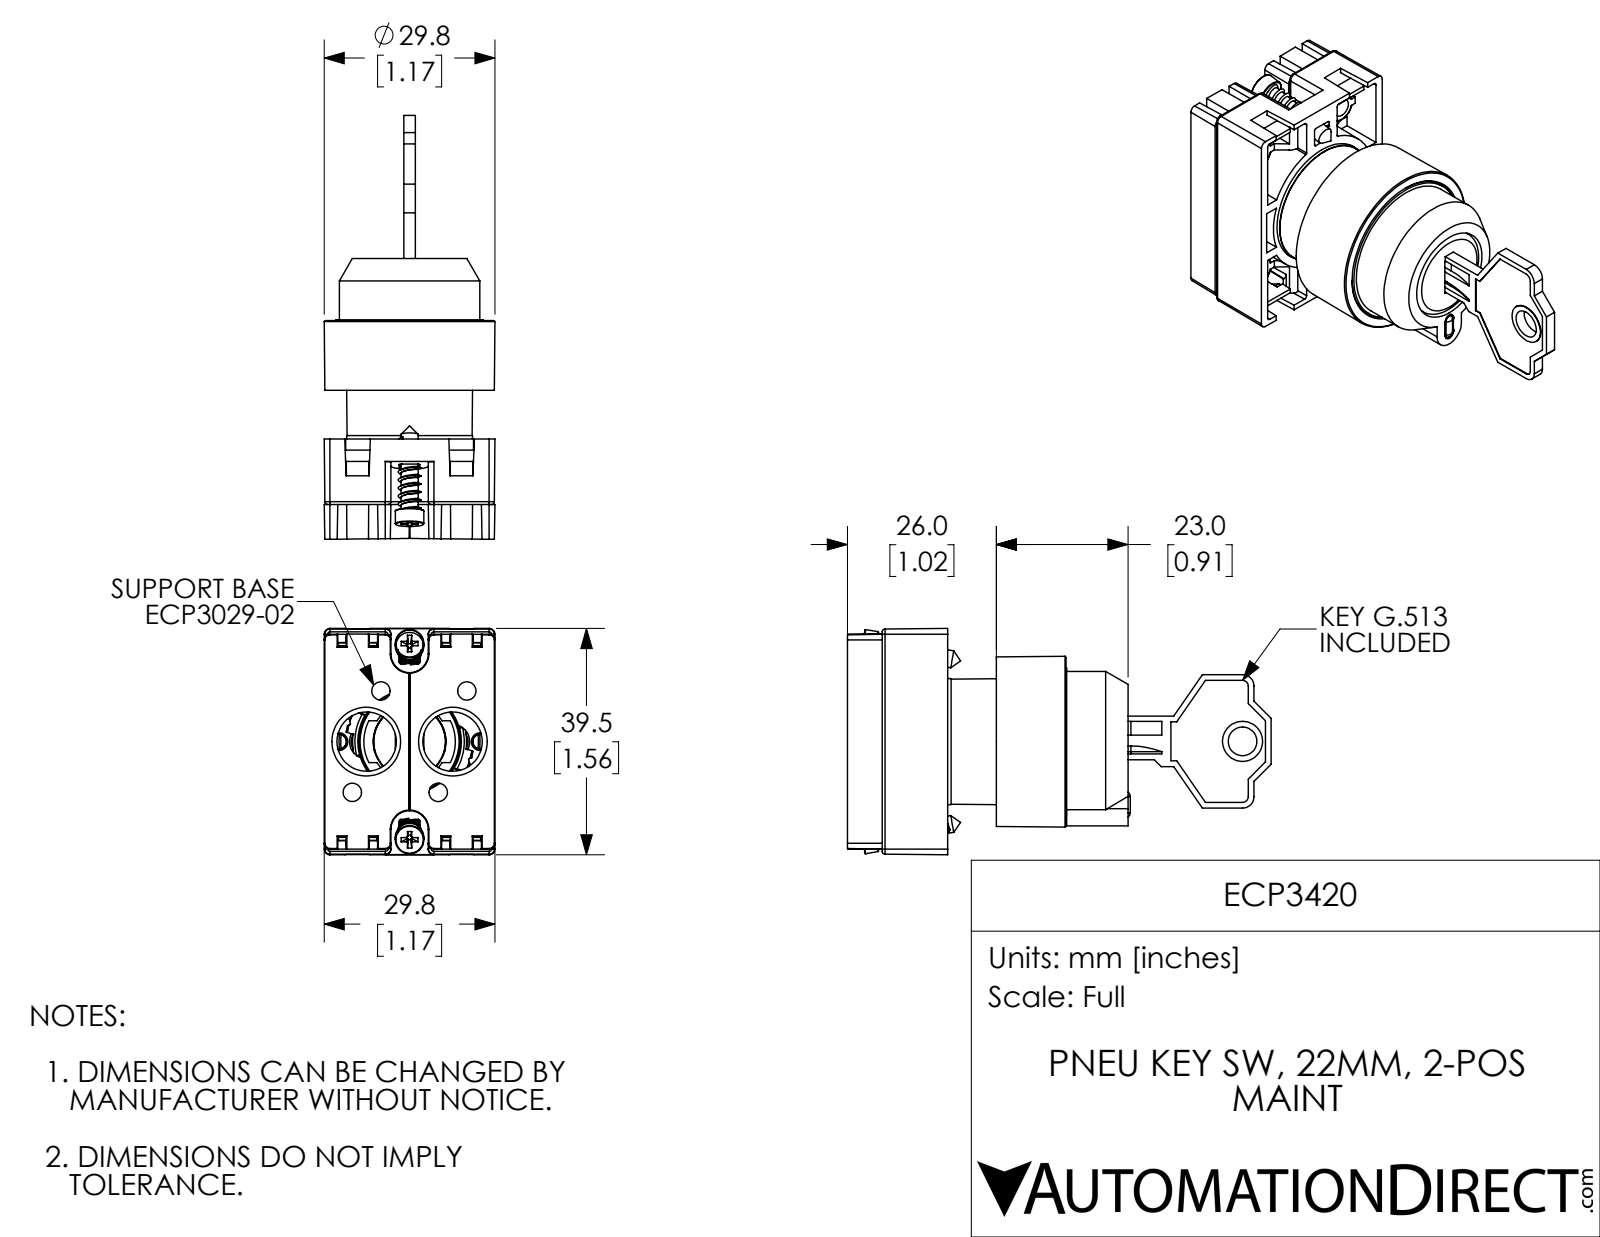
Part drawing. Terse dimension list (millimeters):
name: ECP3420
written by: SolidWorks 2017 (AUTOMOTIVE_DESIGN)
unit: mm
bodies: 10 solids, 961 faces (491 planar, 184 cylindrical, 286 other)
size: 74 × 39.5 × 29.8
volume: 20 340 mm³; area: 23 470 mm²
holes: 4× ⌀2.1, 2× ⌀10.3, 1× ⌀2.4, 1× ⌀5, 1× ⌀12.7, 1× ⌀16.1, 1× ⌀17.7, 1× ⌀19.1, 1× ⌀19.1, 1× ⌀21.7, 1× ⌀24.8, 1× ⌀26
bosses: 2× ⌀5, 2× ⌀3, 1× ⌀25.7, 1× ⌀24.5, 1× ⌀22, 1× ⌀21.6, 1× ⌀15.7, 1× ⌀12.5
rounds: 18× R0.5, 12× R1, 10× R0.3, 8× R0.2, 4× R0.2, 3× R3, 2× R0.2, 2× R2
face distances: 2, 1.7, 1.9, 2.1, 18.2, 21, 11.5, 14.9, 24.5, 2.6
hole spacings: 7.7, 13.7, 20.8, 7.5, 12, 24.7, 27.5, 15
